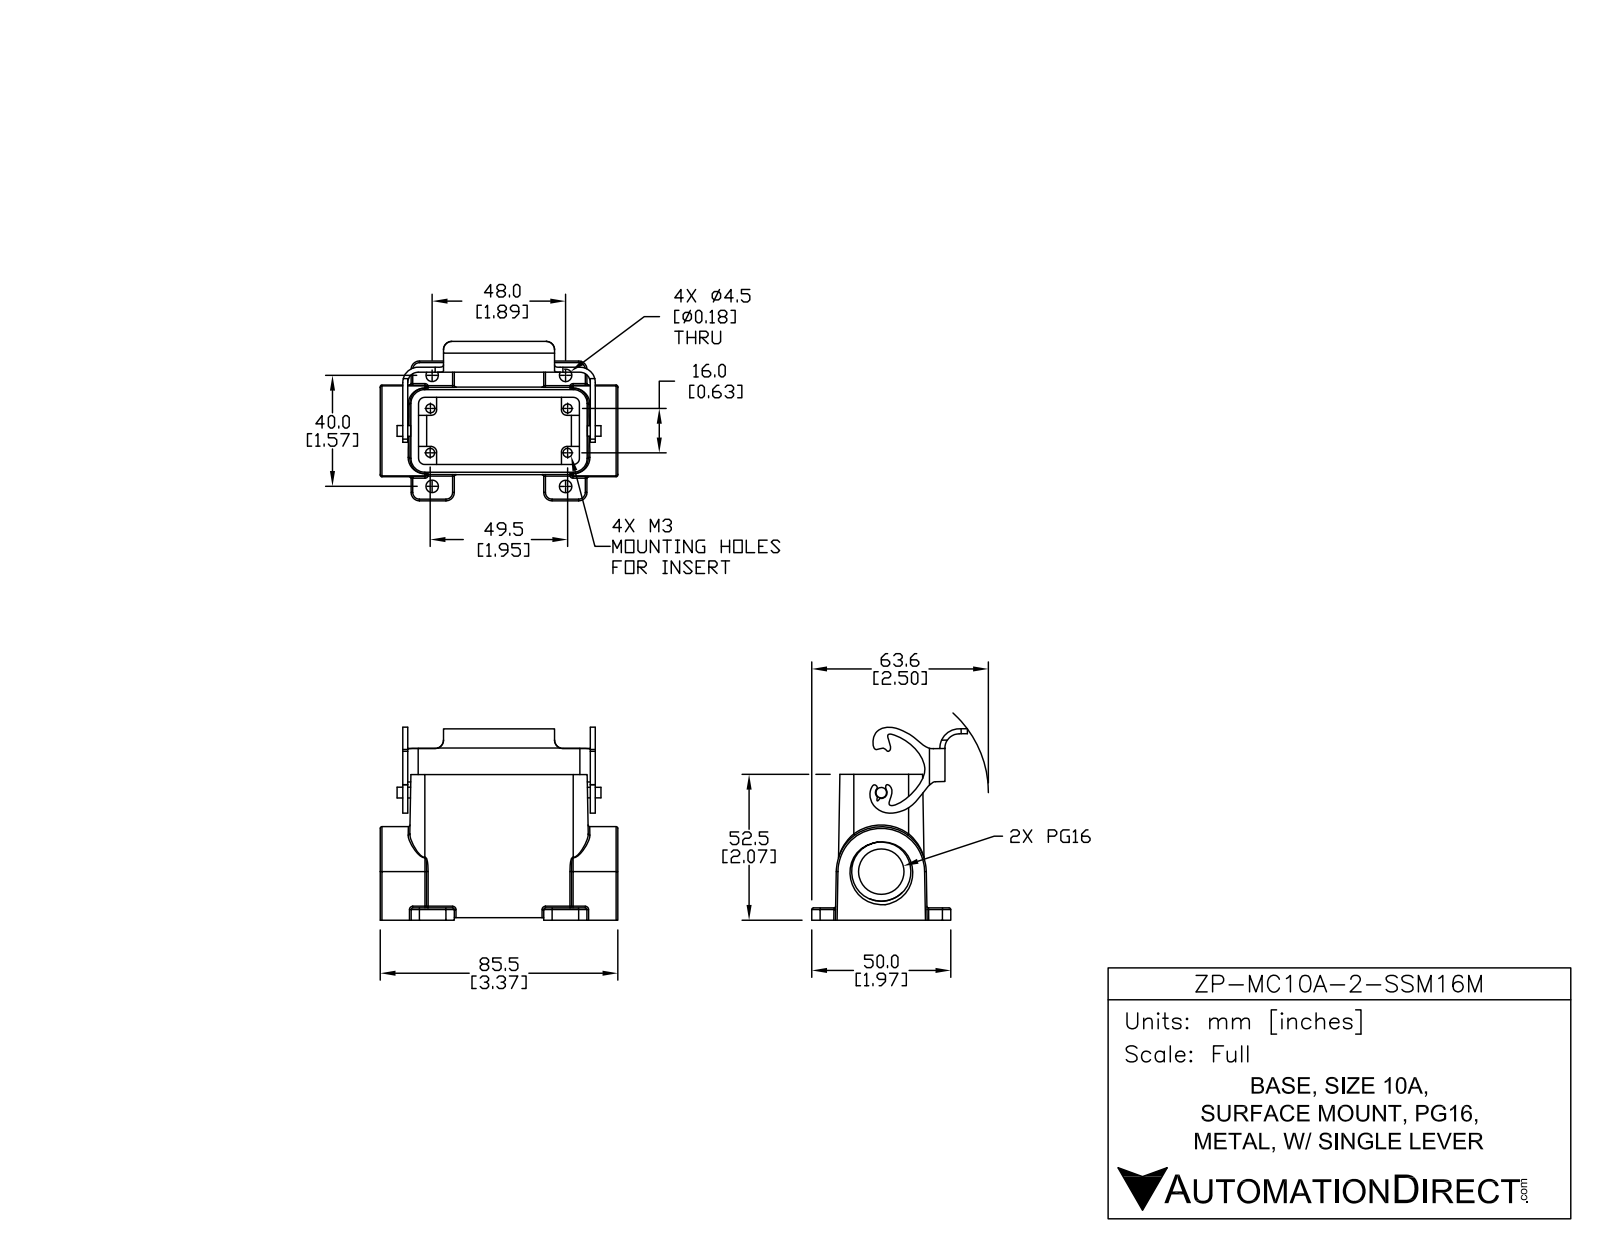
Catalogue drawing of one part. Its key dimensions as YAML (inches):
part_name: "ZP-MC10A-2-SSM16M"
step_written_by: "SolidWorks 2014 (AUTOMOTIVE_DESIGN)"
units: inches
bodies: {solids: 2, faces: 272, planar: 91, cylindrical: 111, other: 70}
overall_size: [3.366, 2.735, 2.248]
volume: 3.32
surface_area: 51.53
round_holes:
  - {diameter: 0.118, count: 4}
  - {diameter: 0.177, count: 4}
  - {diameter: 0.643, count: 1}
  - {diameter: 0.839, count: 1}
round_bosses_or_shafts:
  - {diameter: 0.154, count: 1}
  - {diameter: 0.15, count: 1}
partial_cylinders:
  - {radius: 0.024, count: 32}
  - {radius: 0.118, count: 12}
  - {radius: 0.079, count: 4}
  - {radius: 0.148, count: 2}
  - {radius: 0.219, count: 2}
  - {radius: 0.083, count: 1}
  - {radius: 0.201, count: 1}
  - {radius: 0.272, count: 1}
face_to_face_distances: [0.109, 0.109, 0.175, 0.139, 0.071, 0.036, 0.787, 2.579, 2.028, 3.366]
hole_center_spacings: [0.473, 1.103, 1.977, 2.213, 0.63, 1.575, 1.89, 1.949]
